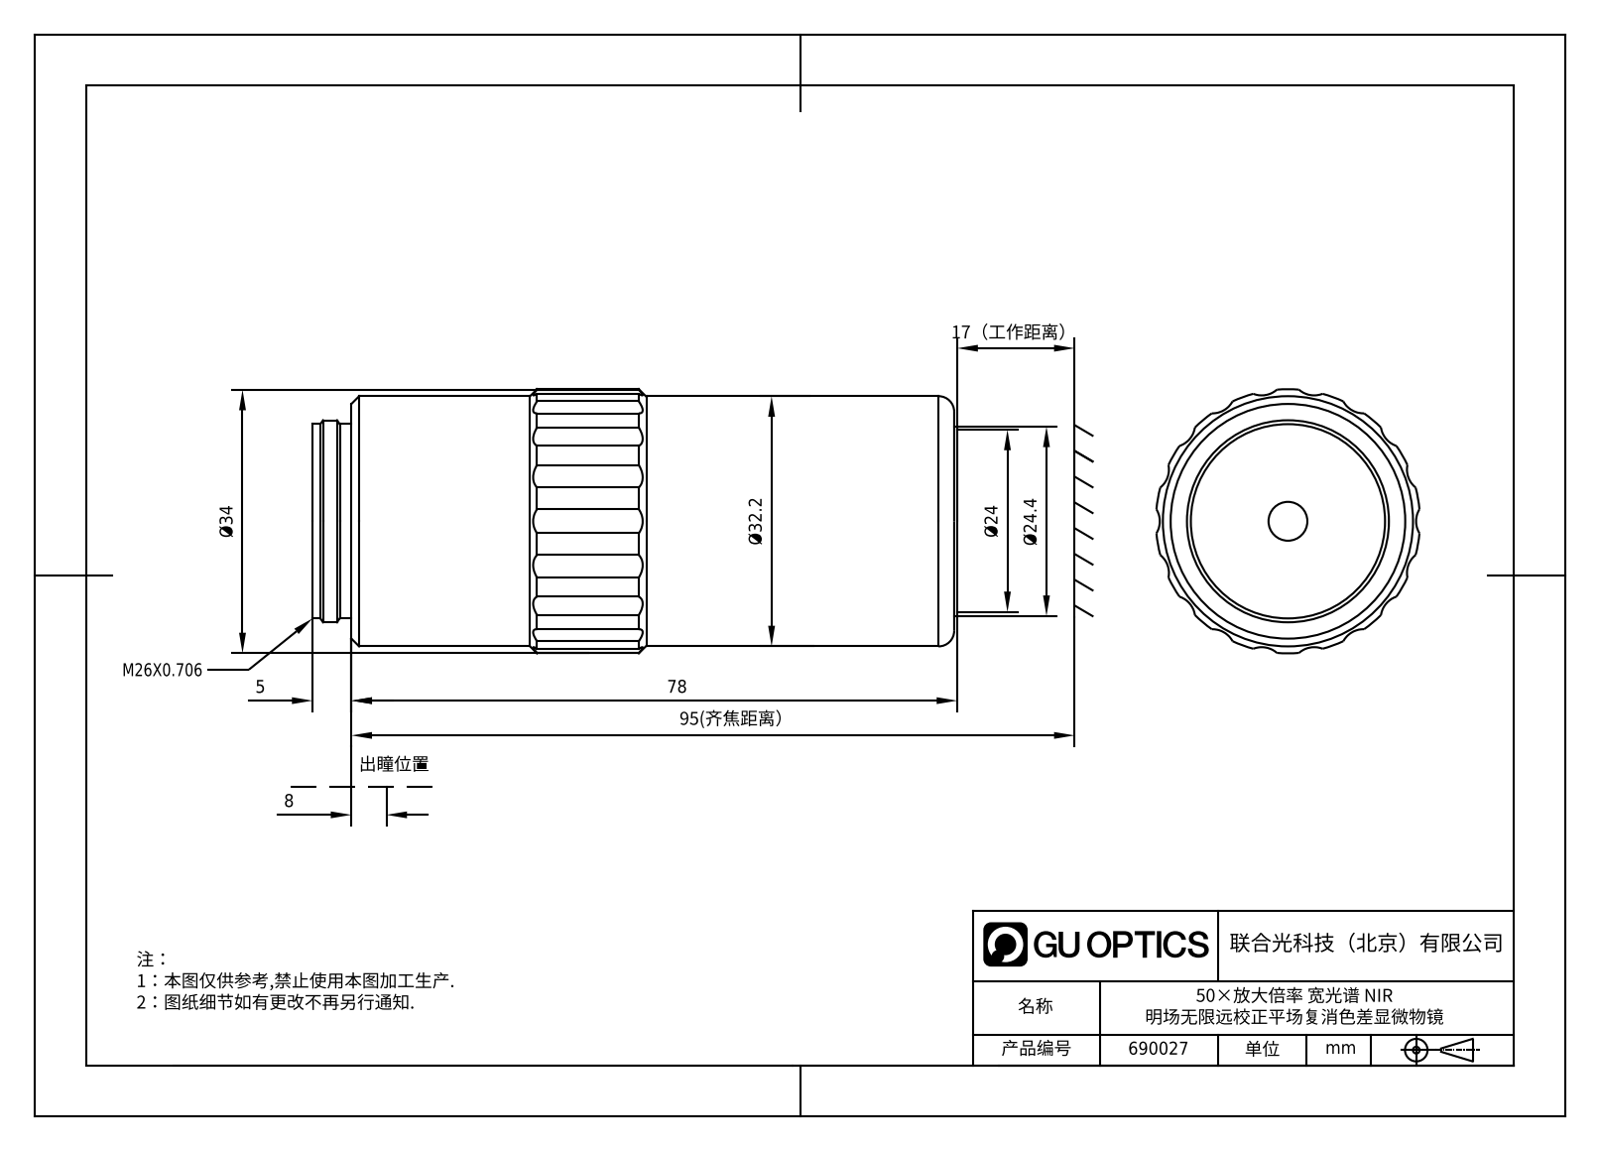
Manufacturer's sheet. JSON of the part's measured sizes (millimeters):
{"part_name": "MPA-NIR50x_378-825-5_1; 690027_1", "step_written_by": "SolidWorks 2020 (CONFIG_CONTROL_DESIGN)", "units": "millimeters", "bodies": {"solids": 1, "faces": 57, "planar": 7, "cylindrical": 44, "other": 6}, "overall_size": [83, 34, 33.86], "volume_mm3": 66655, "surface_area_mm2": 10041, "round_holes": [[5, 1], [20.5, 1]], "round_bosses_or_shafts": [[32.2, 1], [26, 1], [25, 1], [24.4, 1]], "partial_cylinders_radius": [[3, 18], [17, 1]], "face_to_face_distances": [82.5, 5, 77.5, 82.6, 77.6, 83, 78, 0.5, 0.4, 1]}
